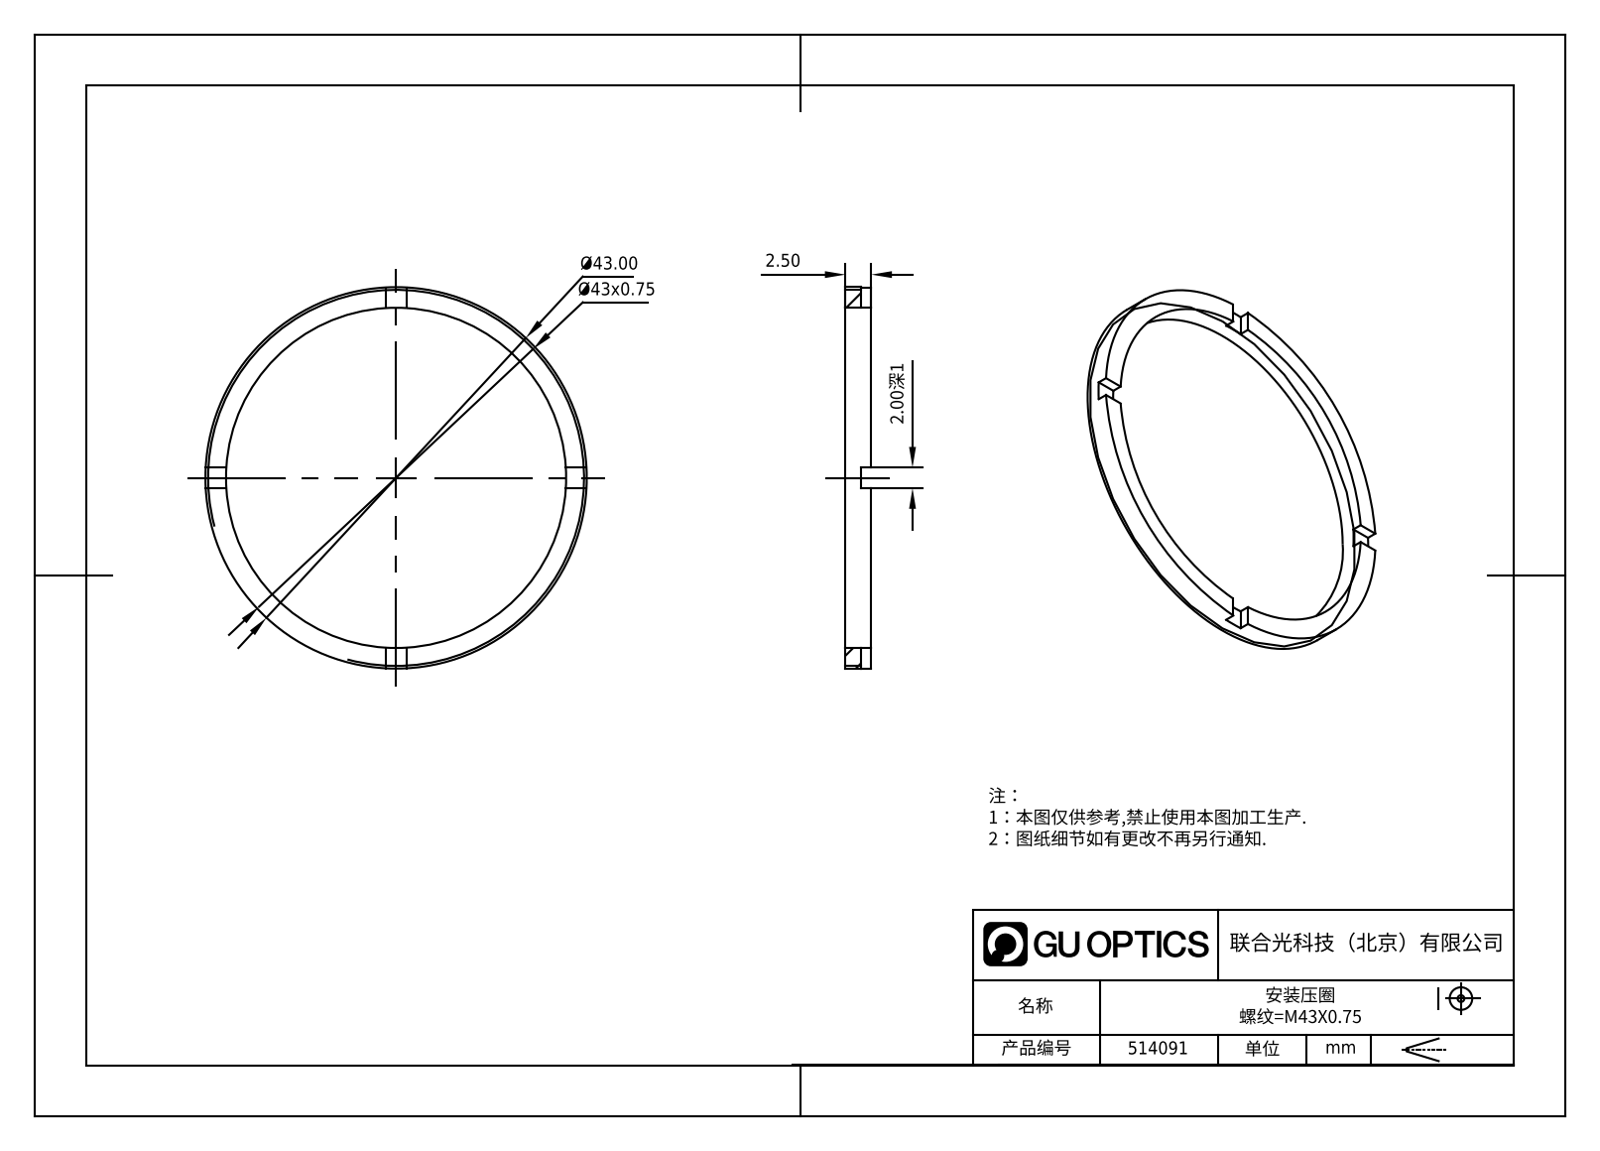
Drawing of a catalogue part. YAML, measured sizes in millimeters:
part_name: "514091"
step_written_by: "SolidWorks 2020 (CONFIG_CONTROL_DESIGN)"
units: millimeters
bodies: {solids: 1, faces: 21, planar: 17, cylindrical: 4, other: 0}
overall_size: [43, 43, 2.5]
volume: 628
surface_area: 1159
round_holes:
  - {diameter: 39, count: 1}
round_bosses_or_shafts:
  - {diameter: 43, count: 1}
face_to_face_distances: [2.5, 1.5, 1, 2]
